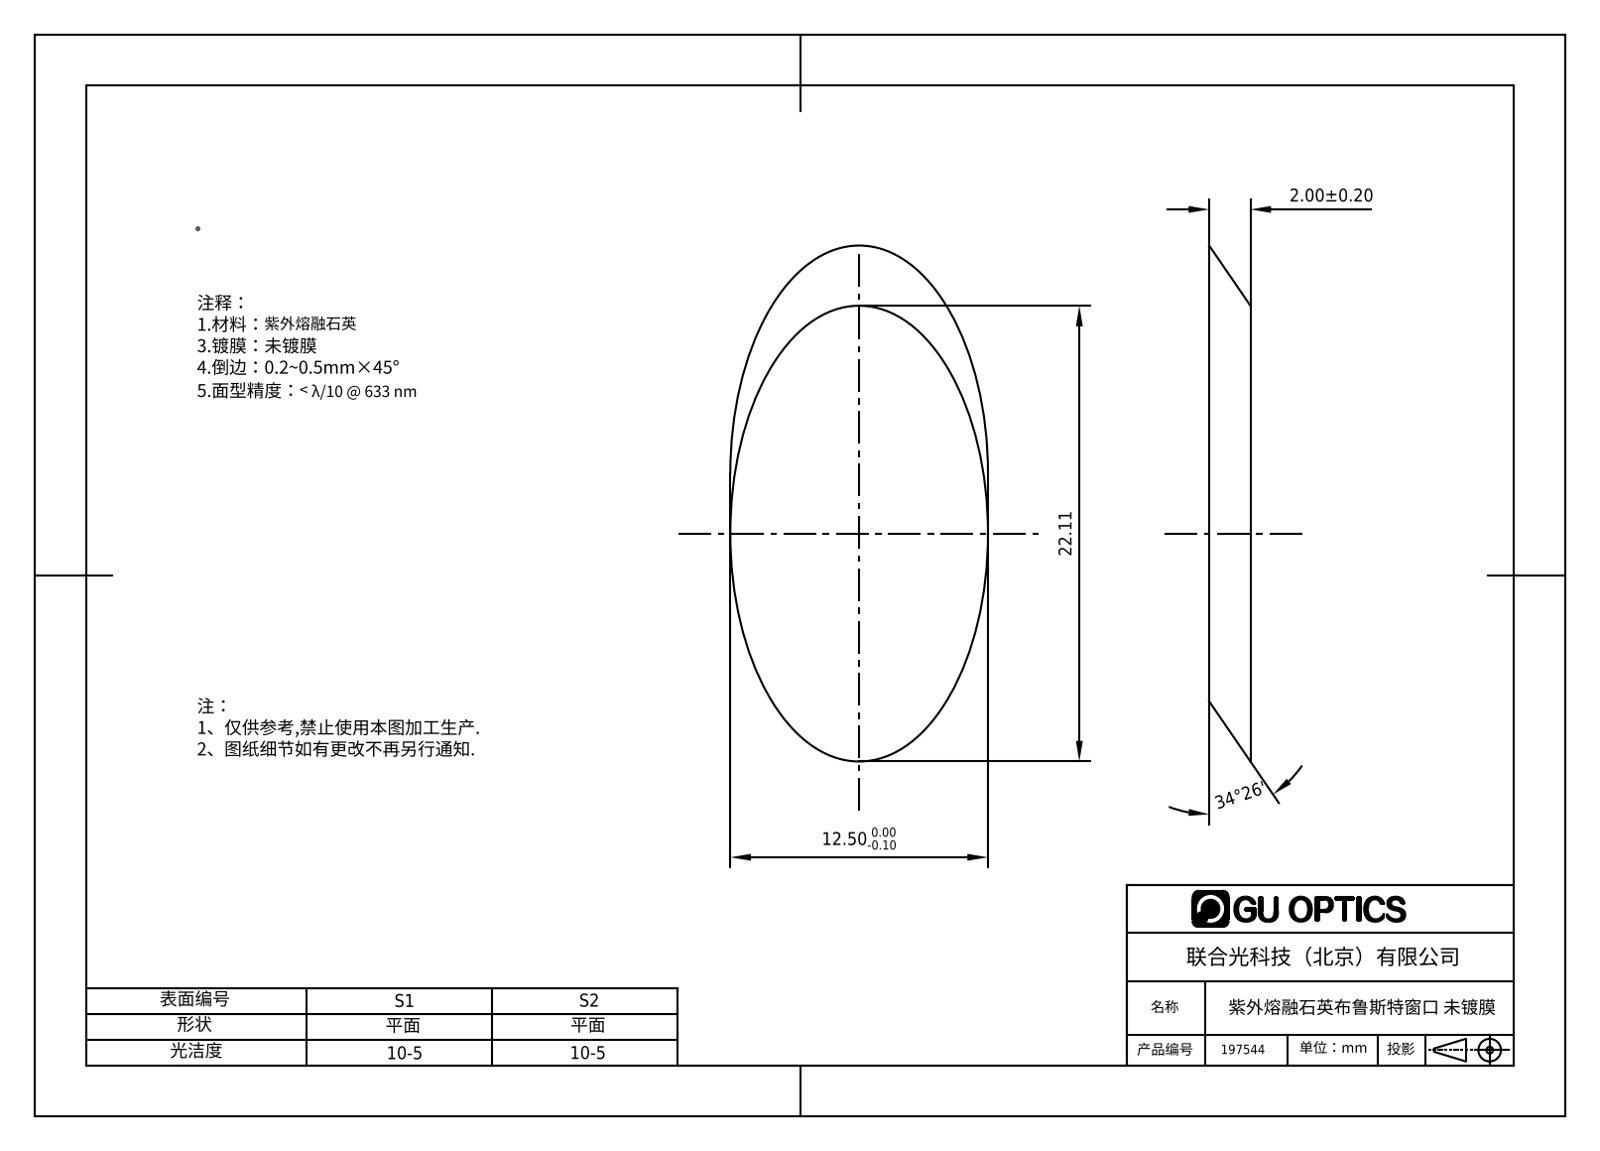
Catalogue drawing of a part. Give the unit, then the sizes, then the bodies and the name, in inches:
Units: inches
Overall size (bounding box): 0.985 × 0.492 × 0.079
Round bosses / shafts (diameter × count): ⌀0.492 ×1
Main face-to-face distances: 0.079
Volume: 0.026 in³ · Surface area: 0.888 in²
Bodies: 1 solid, 4 faces (2 planar, 2 cylindrical, 0 other)
Part name (STEP PRODUCT): Web Model 65824
STEP written by: SolidWorks 2016 (CONFIG_CONTROL_DESIGN)
